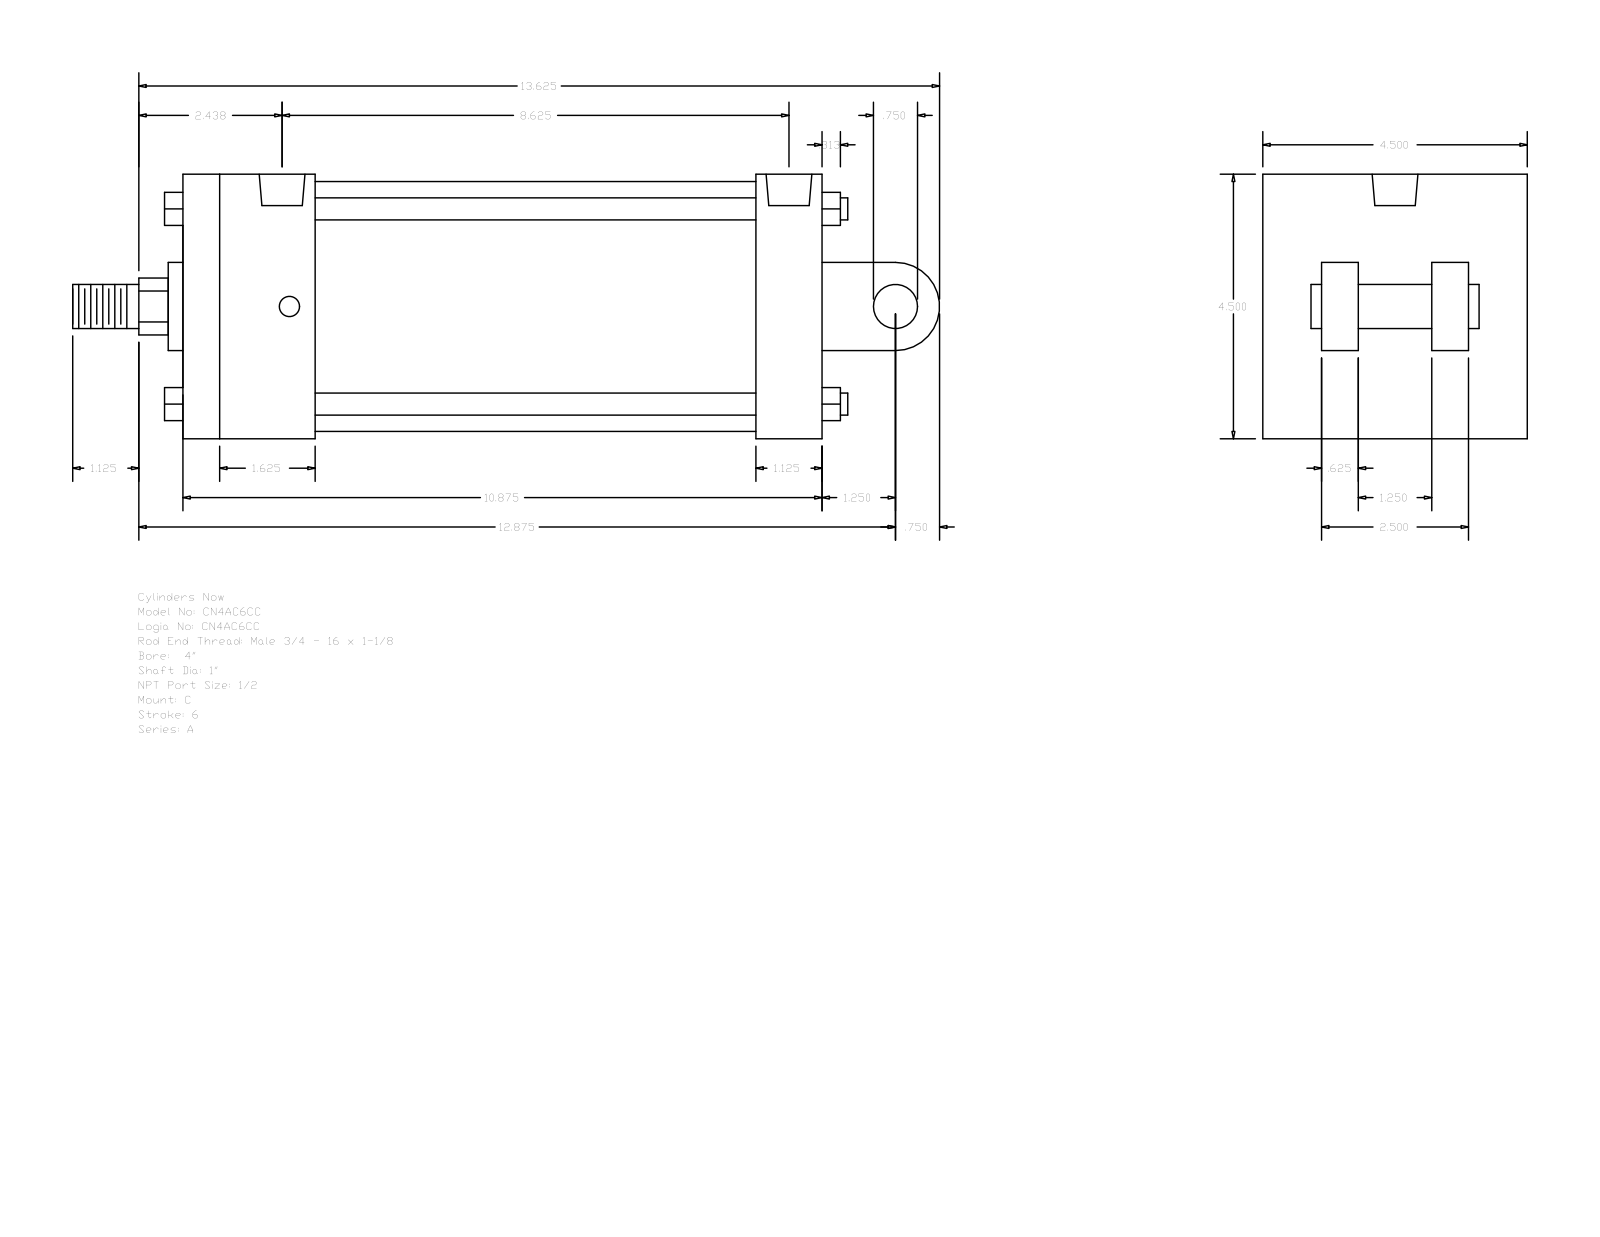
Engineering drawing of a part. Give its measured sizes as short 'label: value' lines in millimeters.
name: A_C__0400_1
written by: GSSL Pune (CONFIG_CONTROL_DESIGN)
unit: mm
bodies: 0 solids, 135 faces (102 planar, 33 cylindrical, 0 other)
size: 374.65 × 114.3 × 114.3
holes: 4× ⌀8.73, 2× ⌀19.77
bosses: 4× ⌀9.53, 2× ⌀19.05, 1× ⌀107.95, 1× ⌀38.1, 1× ⌀25.4
rounds: 1× R12.29, 1× R19.05
face distances: 114.3, 276.22, 73.03, 28.57, 247.65, 57.15, 190.5, 219.07, 41.27, 38.1
hole spacings: 3.18, 212.72, 215.9, 219.08
